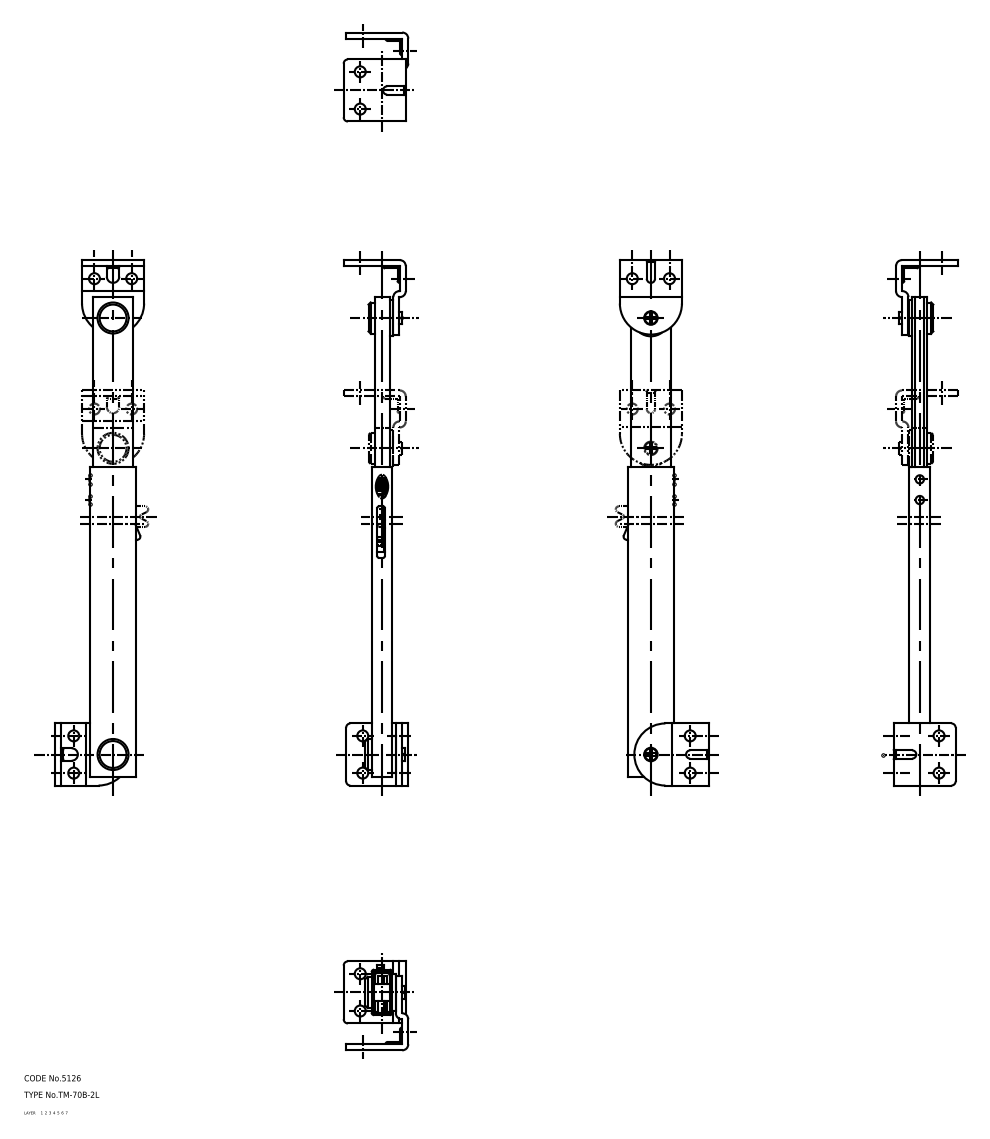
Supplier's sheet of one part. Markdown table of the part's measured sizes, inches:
| quantity | value |
| --- | --- |
| part name | bracket_A_mr-1; rivet_3_mr; rivet_2_mr; rivet_1_mr (+8 more) |
| STEP written by | CADfix (AUTOMOTIVE_DESIGN) |
| units | inches |
| bodies | 12 solids, 299 faces (0 planar, 0 cylindrical, 299 other) |
| overall size | 10 × 1.693 × 1.228 |
| volume | 2.072 in³ |
| surface area | 65.91 in² |
